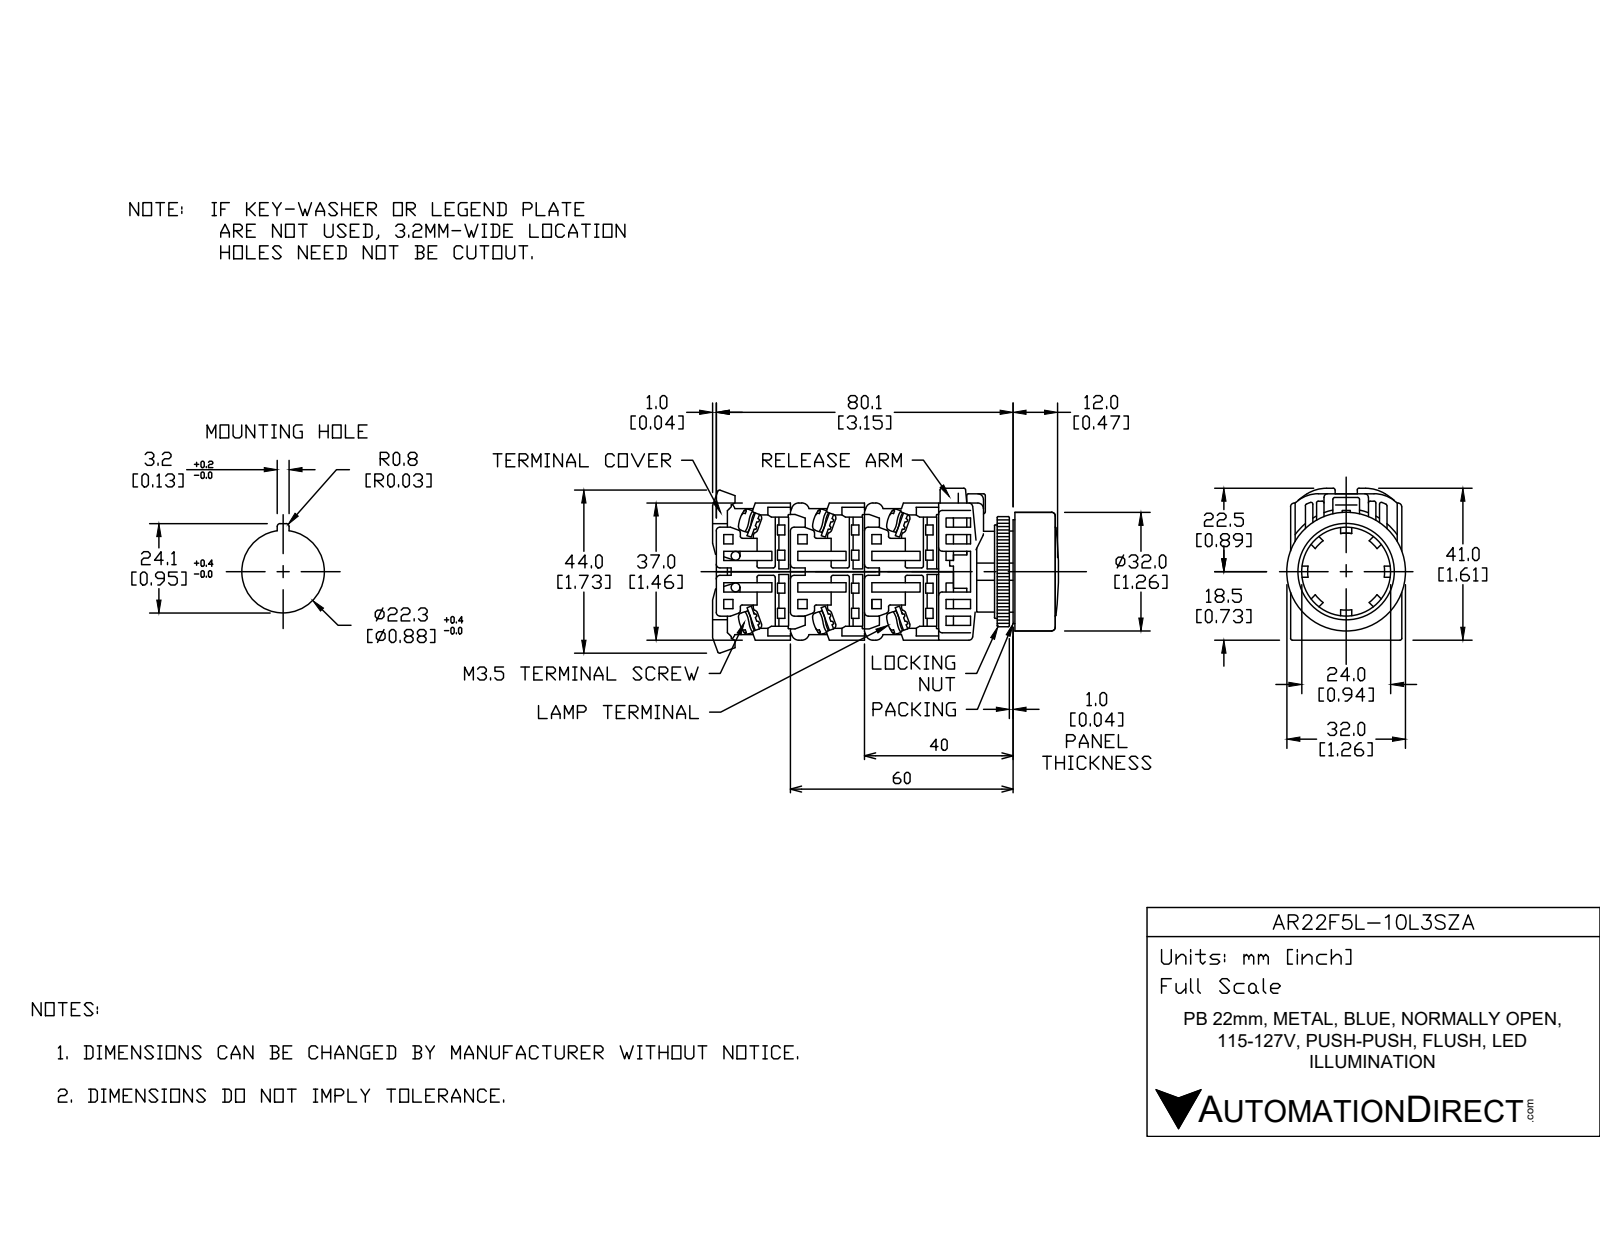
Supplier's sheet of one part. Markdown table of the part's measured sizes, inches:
| quantity | value |
| --- | --- |
| part name | AR22F5L-10L3SZA |
| STEP written by | SolidWorks 2017 (AUTOMOTIVE_DESIGN) |
| units | inches |
| bodies | 16 solids, 451 faces (317 planar, 99 cylindrical, 35 other) |
| overall size | 2.864 × 1.725 × 1.26 |
| volume | 2.9 in³ |
| surface area | 39.87 in² |
| round holes (diameter × count) | 0.858 × 1, 0.866 × 1, 0.984 × 1, 1.22 × 1 |
| round bosses / shafts (diameter × count) | 0.197 × 4, 1.26 × 1, 1.201 × 1, 1.173 × 1, 0.945 × 1, 0.937 × 1, 0.856 × 1, 0.669 × 1 |
| partial cylindrical surfaces (radius × count) | 0.02 × 32, 0.069 × 8, 0.197 × 4, 0.157 × 2, 0.653 × 1, 0.693 × 1 |
| main face-to-face distances | 0.039, 0.709, 1.142, 0.787, 1.122, 0.118, 0.079, 0.827, 0.014, 0.295 |
